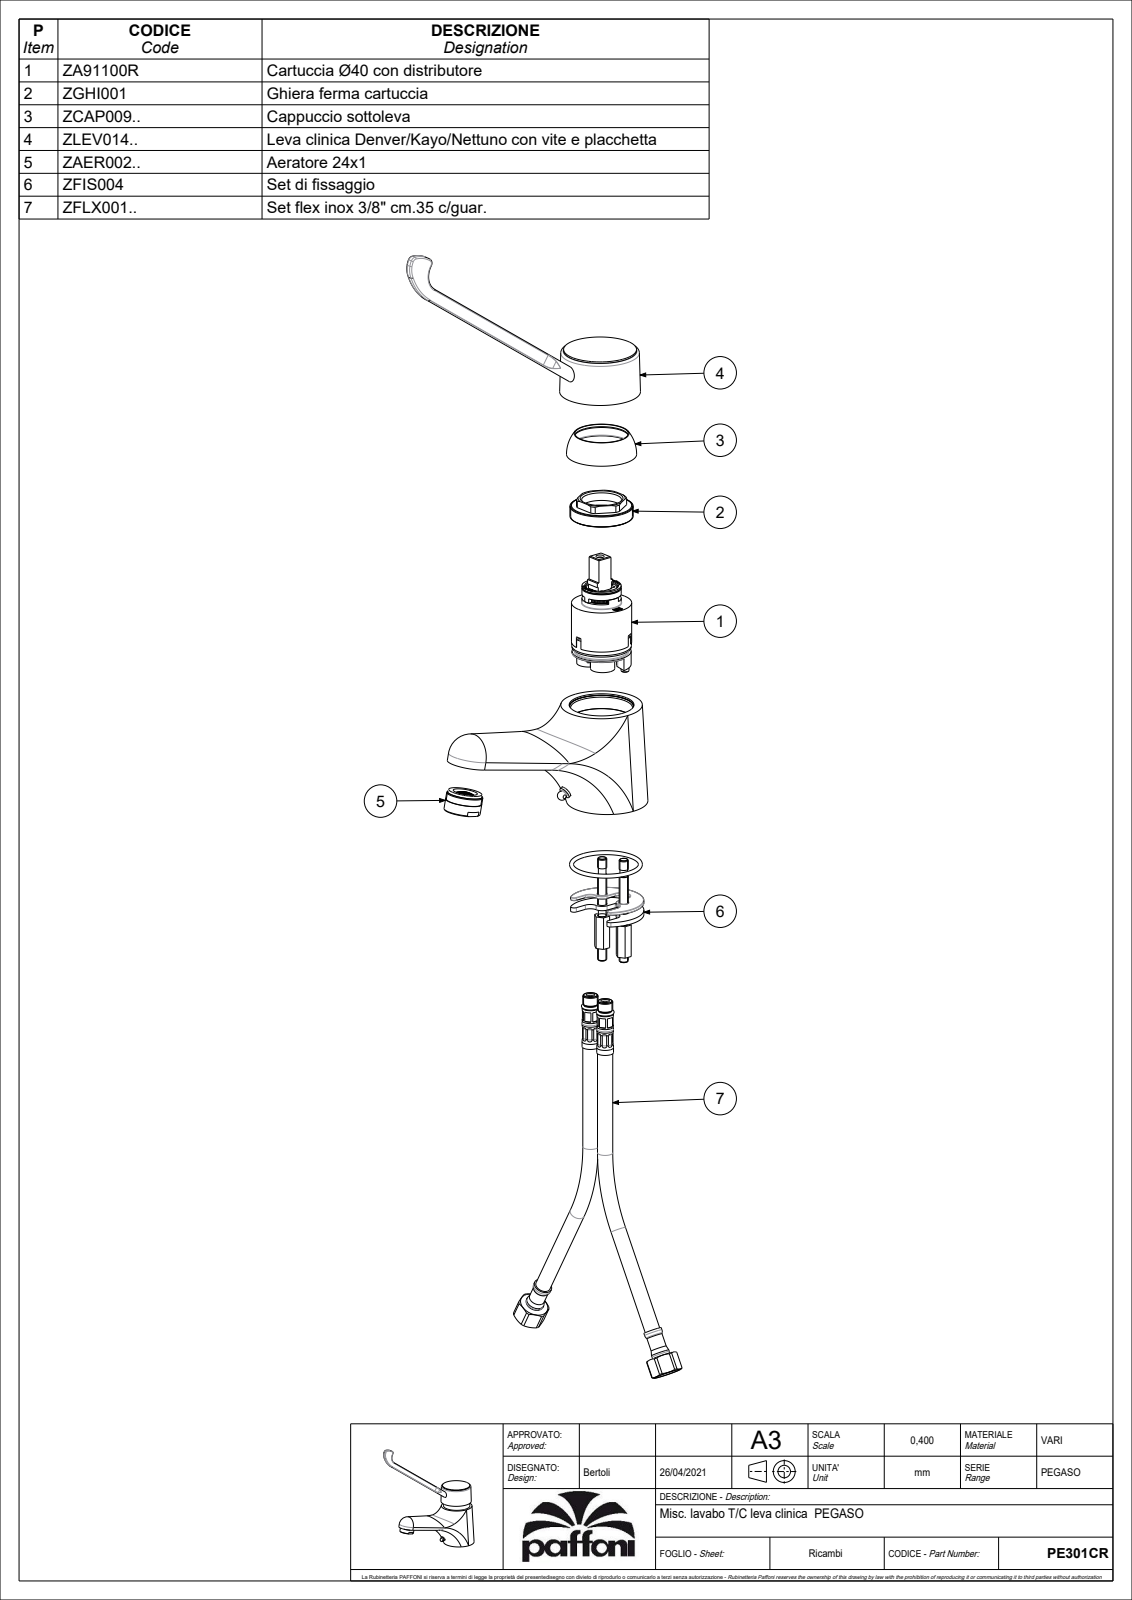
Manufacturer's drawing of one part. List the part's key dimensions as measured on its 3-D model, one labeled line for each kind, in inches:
Part name (STEP PRODUCT): PE301CR_SW0001
STEP written by: CREO PARAMETRIC BY PTC INC, 2022124 (CONFIG_CONTROL_DESIGN)
Units: inches
Bodies: 2 solids, 2121 faces (1704 planar, 205 cylindrical, 212 other)
Overall size (bounding box): 8.212 × 7.645 × 2.106
Volume: 11.21 in³ · Surface area: 118.5 in²
Round holes (diameter × count): ⌀0.315 ×4, ⌀0.433 ×3, ⌀0.217 ×2, ⌀0.276 ×2, ⌀0.354 ×2, ⌀0.472 ×2, ⌀0.591 ×1, ⌀0.63 ×1, ⌀0.669 ×1, ⌀0.787 ×1, ⌀0.827 ×1, ⌀0.906 ×1
Round bosses / shafts (diameter × count): ⌀0.626 ×2, ⌀0.394 ×2, ⌀0.37 ×2, ⌀1.884 ×1, ⌀1.654 ×1, ⌀1.543 ×1, ⌀1.528 ×1, ⌀1.37 ×1
Partial cylindrical surfaces — rounded edges, fillets, slot ends (radius × count): R0.02 ×44, R0.012 ×8, R0.059 ×6, R0.295 ×4, R0.079 ×2, R0.217 ×2, R0.256 ×2, R0.72 ×2
Main face-to-face distances: 0.138, 0.177, 0.118, 0.157, 0.236, 3.031, 0.02, 0.866, 0.61, 0.079
Hole centre spacings: 0.044, 0.39, 0.513, 0.572, 0.079, 0.339, 0.378, 0.432
